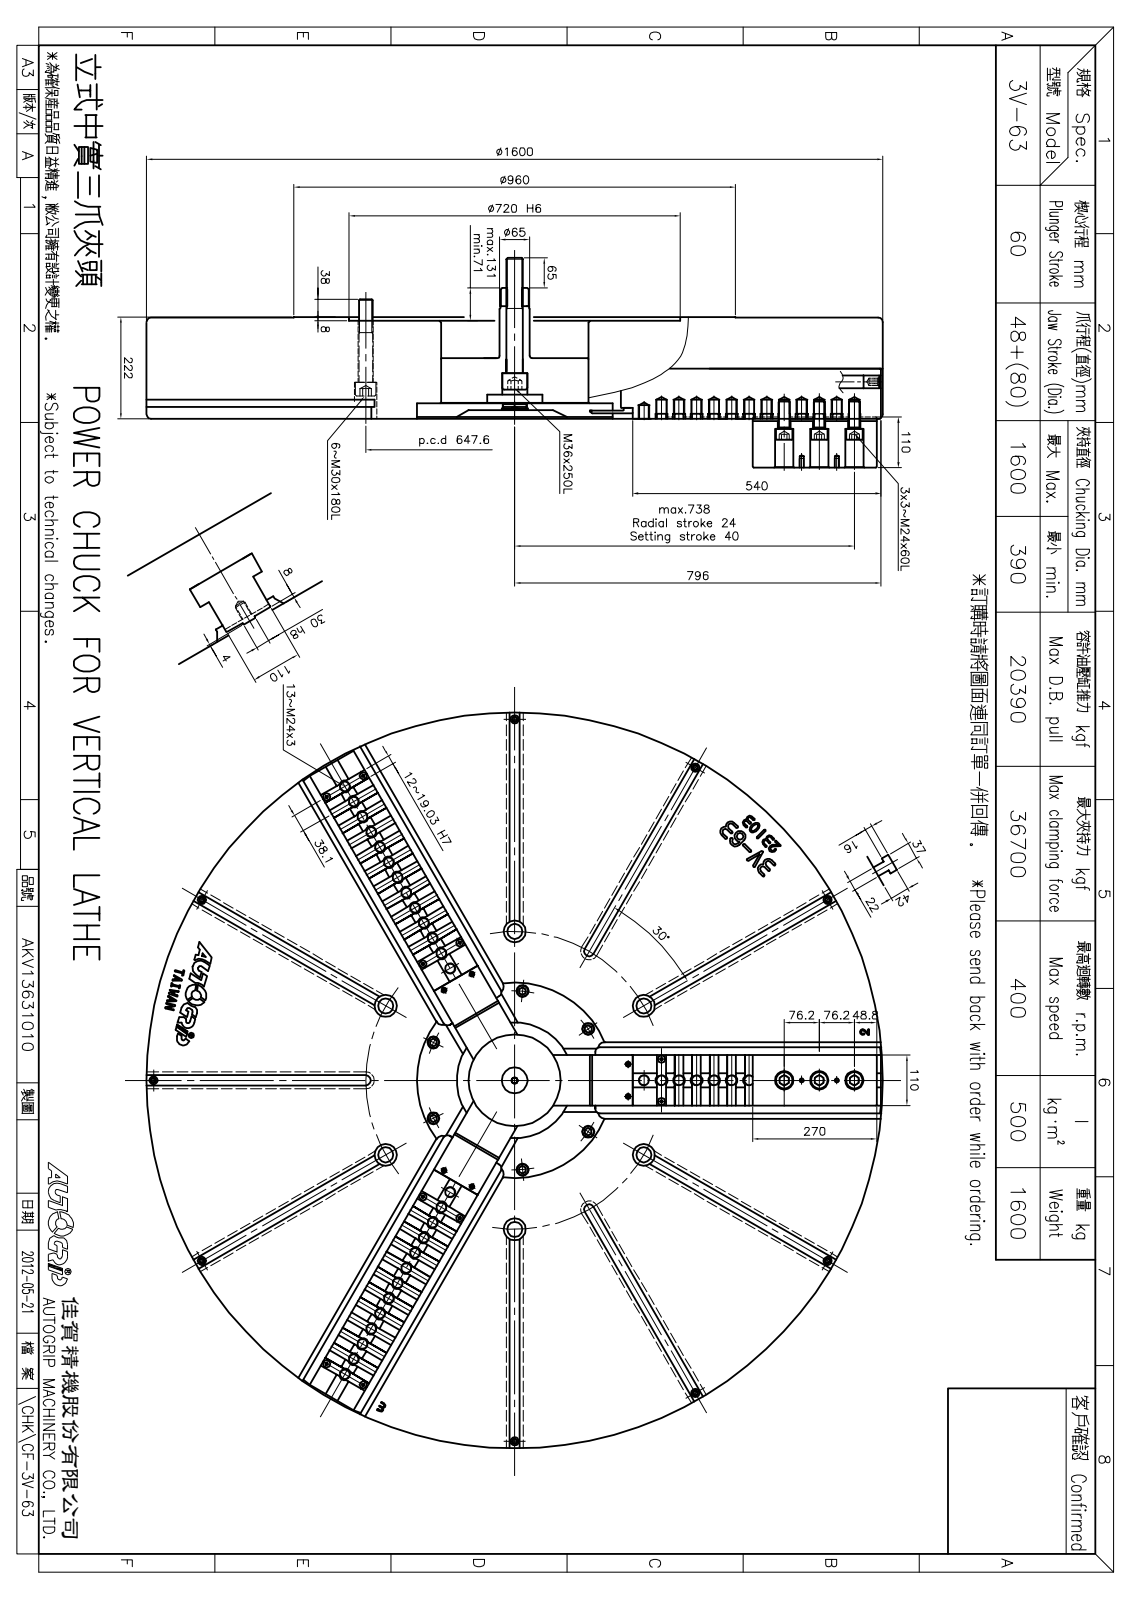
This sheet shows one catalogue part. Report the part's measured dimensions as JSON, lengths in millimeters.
{"part_name": "CF-3V-63; CF-3V-63-01000; 圓頭內六角螺栓_M24x60; CF-3V-63-10000 (+8 more)", "step_written_by": "SolidWorks 2016 (CONFIG_CONTROL_DESIGN)", "units": "millimeters", "bodies": {"solids": 35, "faces": 1681, "planar": 1024, "cylindrical": 398, "other": 259}, "overall_size": [1600, 1600, 456], "volume_mm3": 432900000, "surface_area_mm2": 8788000, "round_holes": [[21, 39], [10.2, 9], [12, 9], [27, 9], [40, 9], [18, 6], [26, 6], [33, 6], [48, 6], [32, 1], [36, 1], [52, 1]], "round_bosses_or_shafts": [[24, 15], [36, 9], [45, 6], [30, 6], [16, 6], [1600, 1], [960, 1], [65, 1]], "partial_cylinders_radius": [[13, 36], [11, 3], [18.5, 3]], "face_to_face_distances": [221, 7, 8, 125, 110, 89, 96, 1, 97, 180], "hole_center_spacings": [785, 38.1, 323.8, 683.29, 987.55, 76.2, 114.3, 152.4]}
